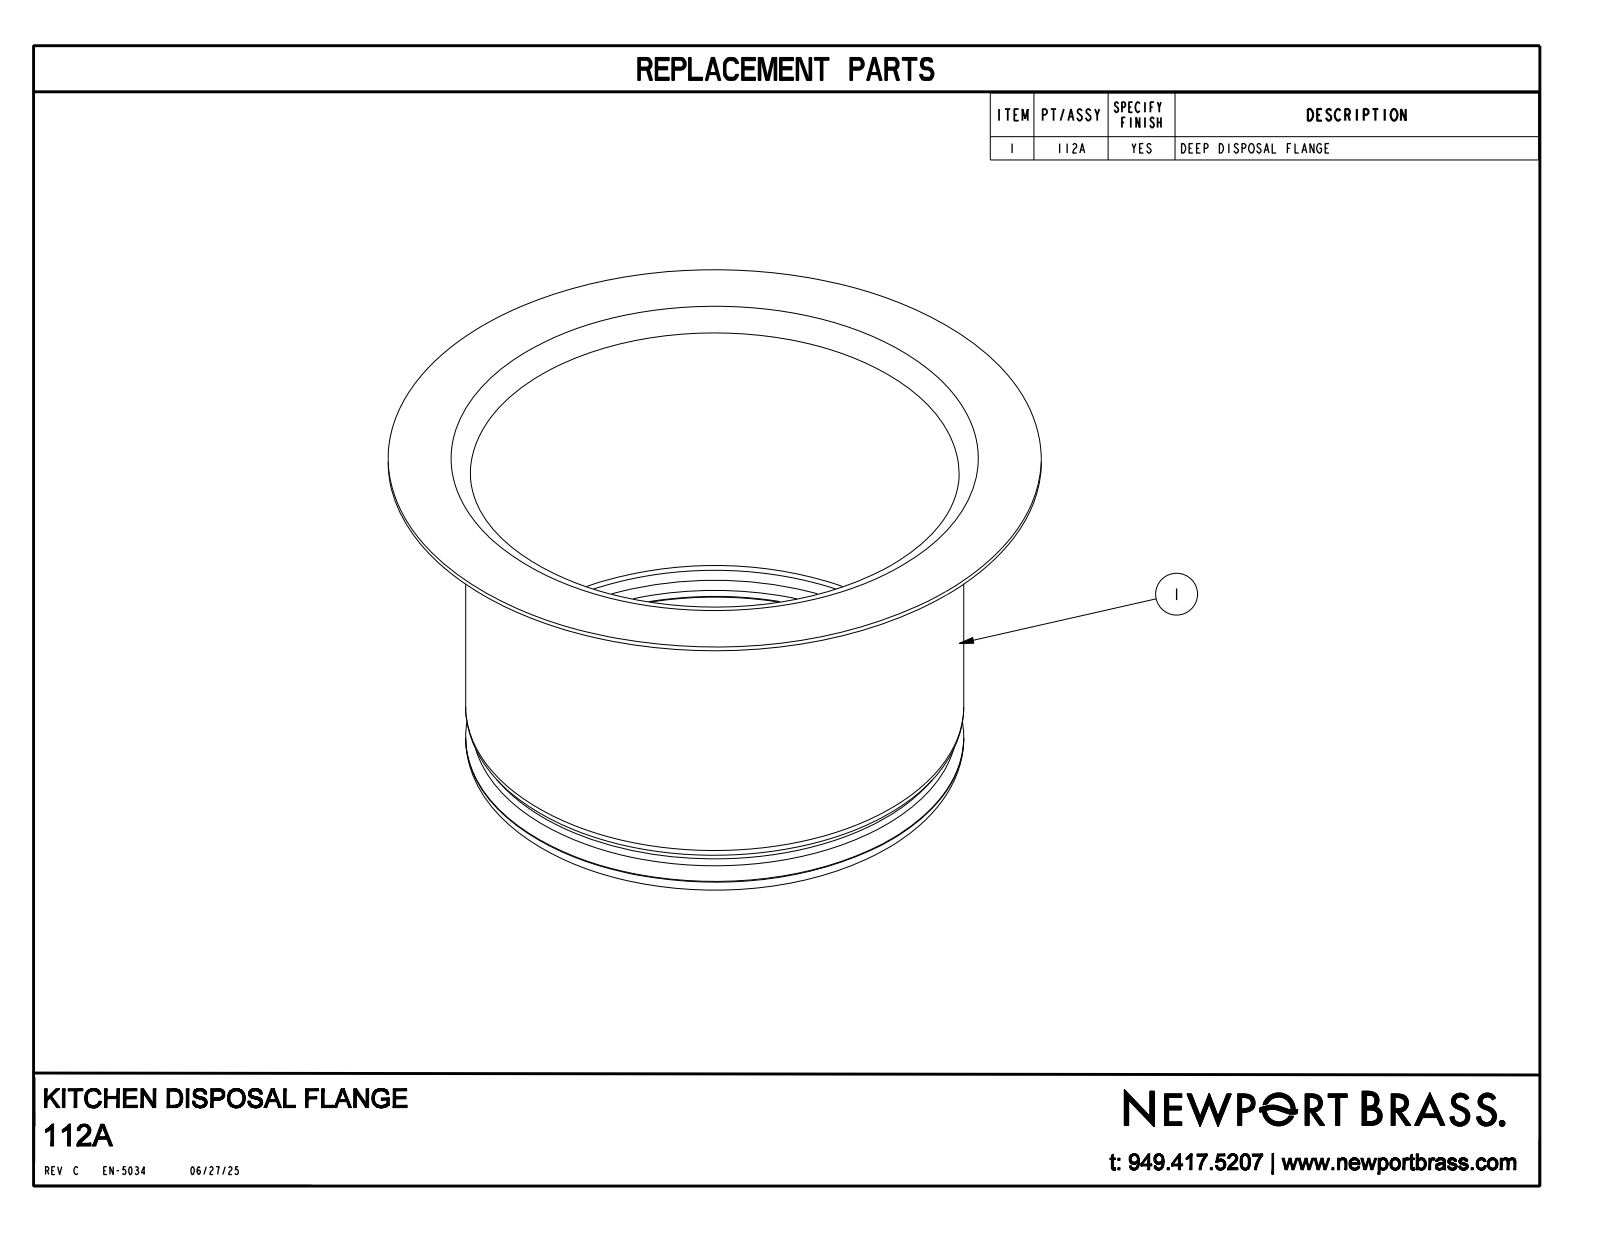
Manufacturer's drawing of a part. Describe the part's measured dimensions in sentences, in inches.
The part is named "50828; 112A_ASM". Its 3-D file was written by "CREO PARAMETRIC BY PTC INC, 2018400 (AUTOMOTIVE_DESIGN)". It is 1 solid with 42 faces: 2 planar, 10 cylindrical and 30 other. Overall it measures 4.49 by 4.49 by 2.5 inches. Its volume is 1.09 cubic inches and its surface area 68.88 square inches. Round holes: 1 of diameter 3.36. Round bosses or shafts: 1 of diameter 4.49, 1 of diameter 3.424. The main face-to-face distances are 0.032.
